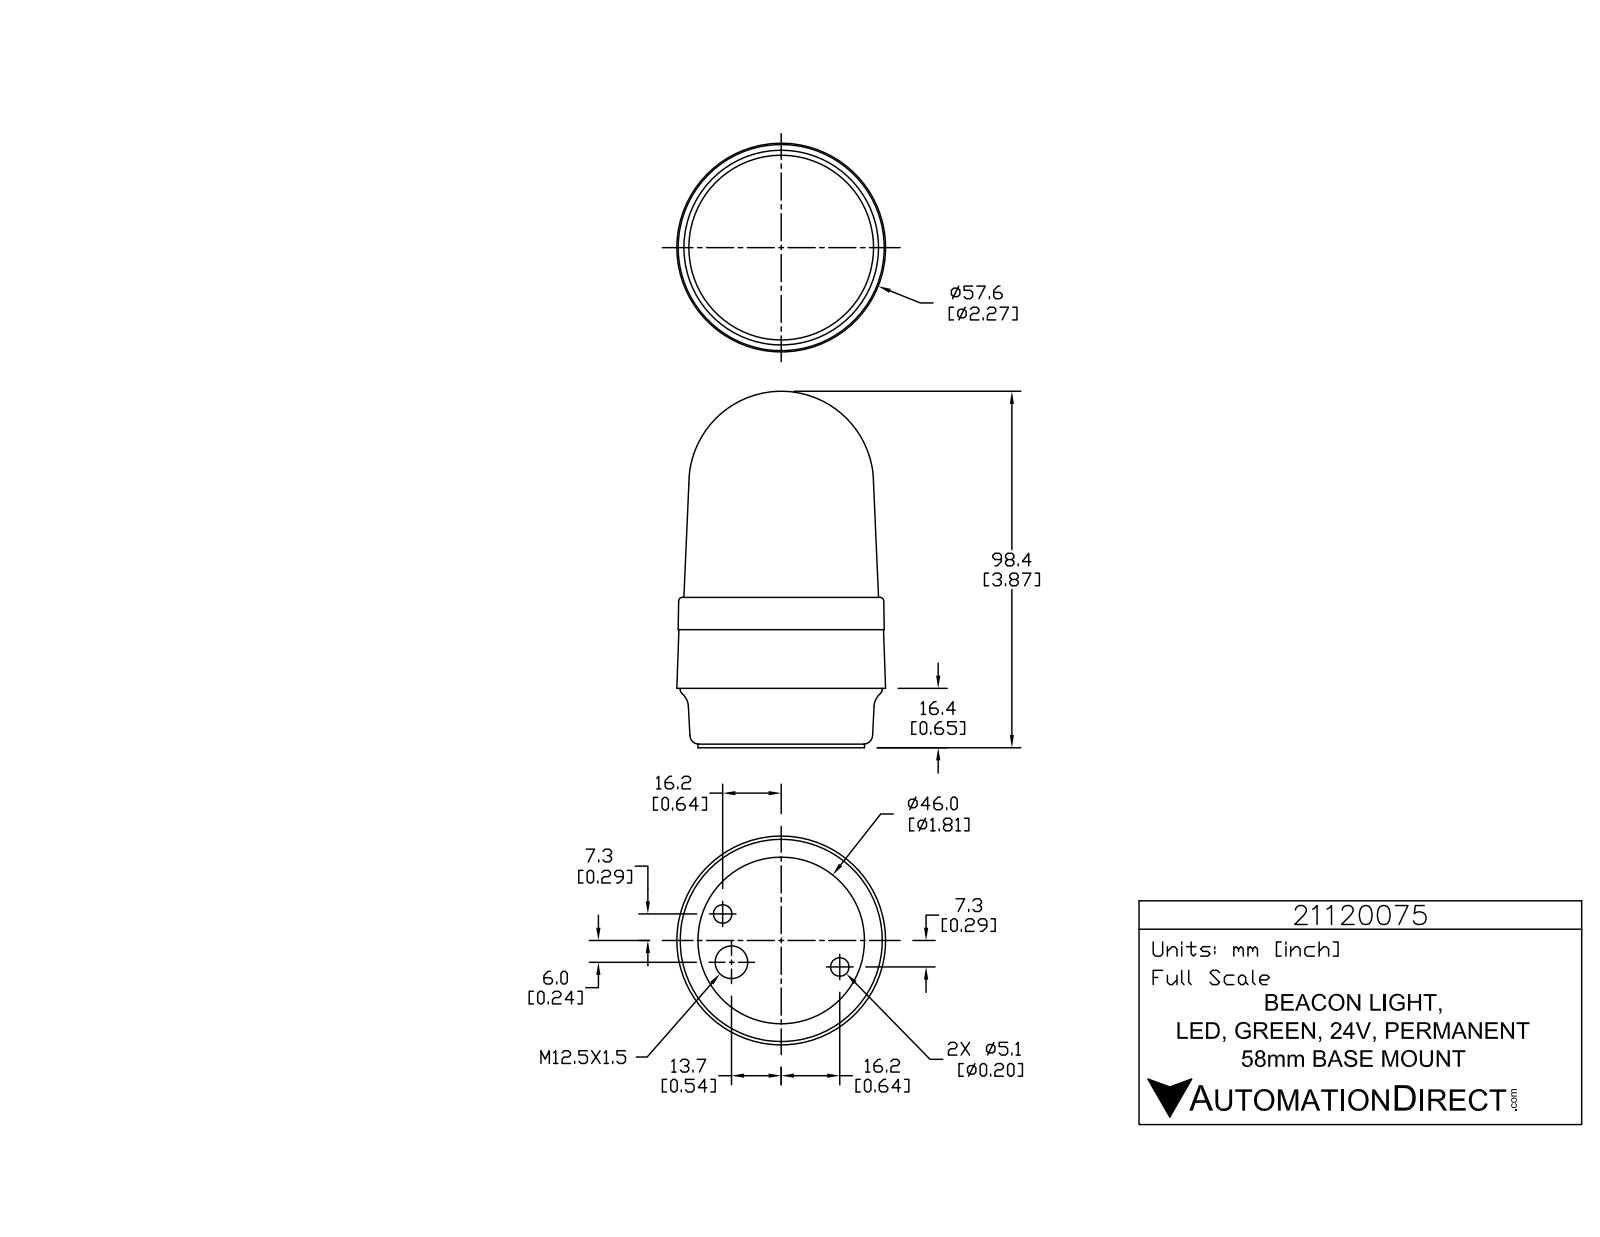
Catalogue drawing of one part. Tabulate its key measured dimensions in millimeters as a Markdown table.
| quantity | value |
| --- | --- |
| part name | 21120075 |
| STEP written by | SolidWorks 2015 (AUTOMOTIVE_DESIGN) |
| units | millimeters |
| bodies | 1 solid, 764 faces (527 planar, 145 cylindrical, 92 other) |
| overall size | 98.4 × 57.63 × 57.63 |
| volume | 199 898 mm³ |
| surface area | 18 922 mm² |
| round holes (diameter × count) | 0.99 × 3, 5.11 × 2, 9 × 1 |
| round bosses / shafts (diameter × count) | 5.74 × 3, 1.43 × 3, 55.8 × 1, 46 × 1 |
| partial cylindrical surfaces (radius × count) | 0.2 × 6, 0.21 × 6, 0.21 × 6, 3.32 × 6, 0.1 × 3, 0.12 × 3, 0.19 × 3, 0.2 × 3 |
| main face-to-face distances | 16.4, 1, 15.4, 41.5, 40.5, 25.1, 32.6, 31.6, 16.2, 8.9 |
| hole center spacings | 13.56, 29.94, 35.5 |
